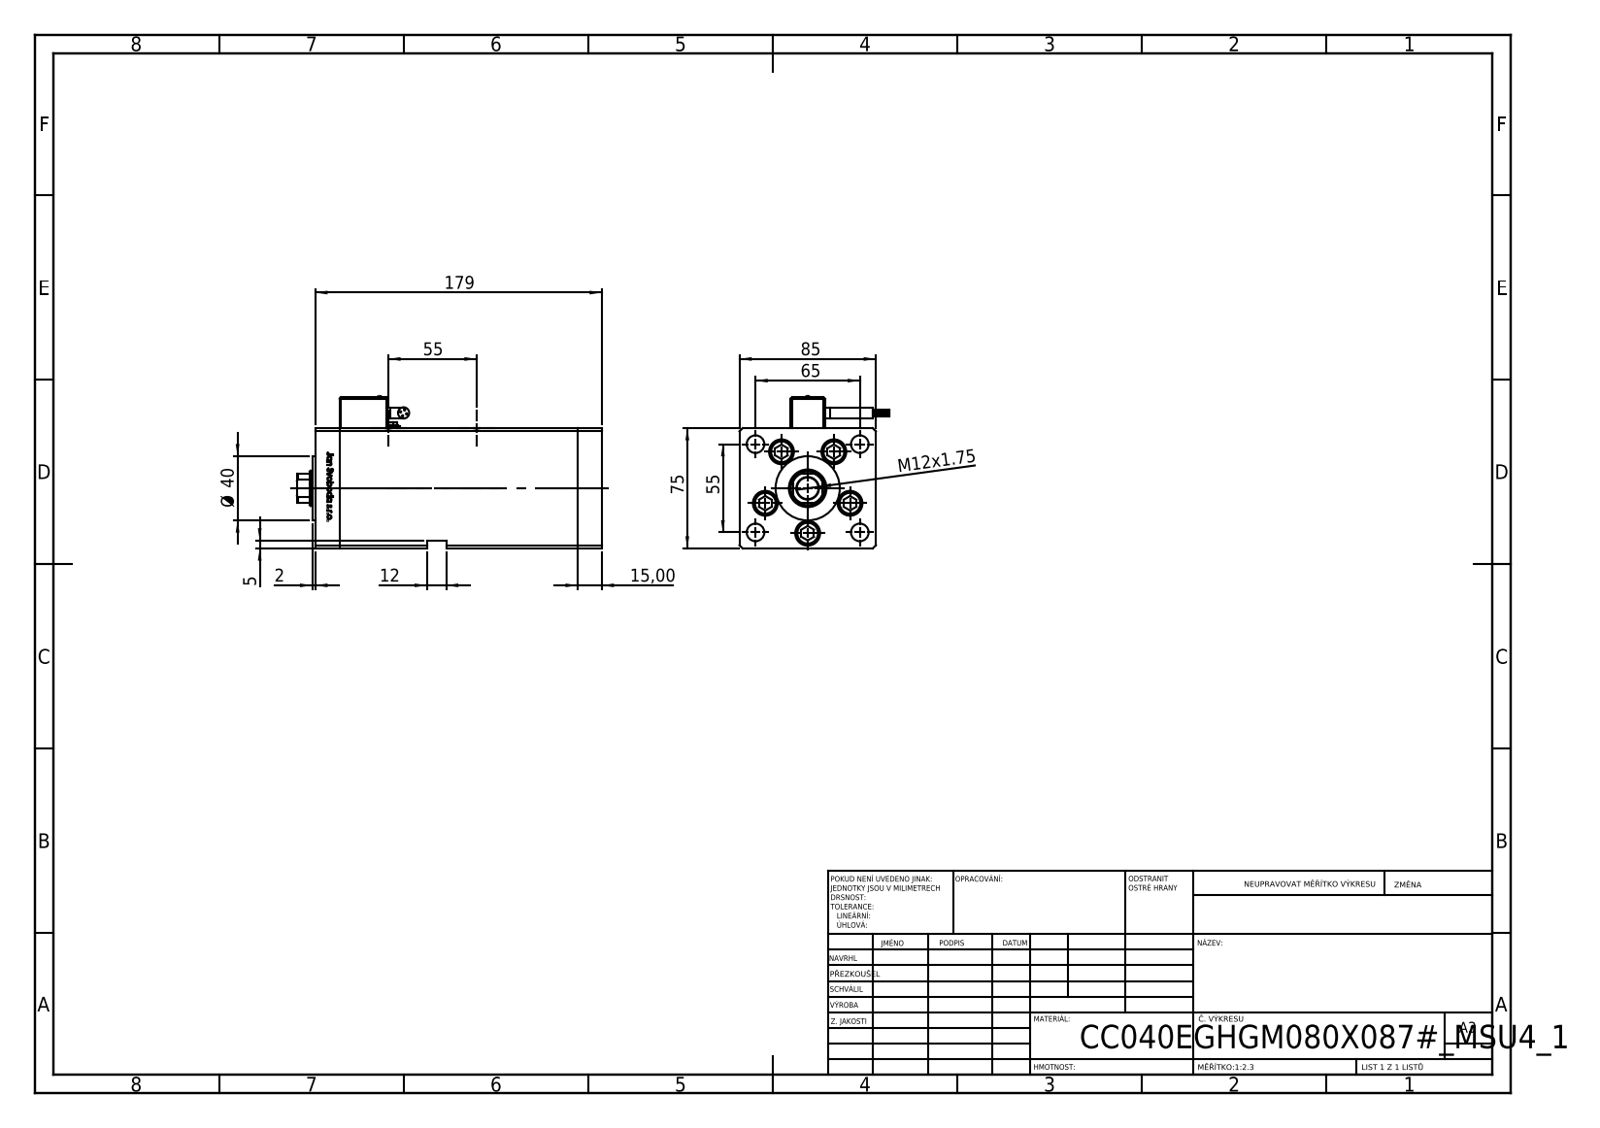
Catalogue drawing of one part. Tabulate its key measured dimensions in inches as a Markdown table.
| quantity | value |
| --- | --- |
| part name | V220C_FRONT_E; V220C_E MIDDLE; V220C BACK_E; Magnetic_Switch_MSU4 (+2 more) |
| STEP written by | SolidWorks 2019 (CONFIG_CONTROL_DESIGN) |
| units | inches |
| bodies | 15 solids, 1314 faces (512 planar, 210 cylindrical, 592 other) |
| overall size | 7.48 × 3.744 × 3.673 |
| volume | 60.35 in³ |
| surface area | 275.6 in² |
| round holes (diameter × count) | 0.433 × 9, 0.61 × 5, 0.413 × 4, 0.65 × 4, 0.079 × 2, 0.518 × 2, 0.142 × 1, 0.197 × 1, 0.276 × 1, 0.531 × 1, 0.866 × 1, 0.925 × 1 |
| round bosses / shafts (diameter × count) | 0.571 × 5, 0.315 × 5, 0.033 × 4, 0.276 × 2, 1.575 × 1, 0.236 × 1, 0.138 × 1, 0.098 × 1 |
| partial cylindrical surfaces (radius × count) | 0.039 × 14, 0.037 × 2, 0.157 × 2, 0.413 × 1 |
| main face-to-face distances | 3.346, 2.953, 0.591, 5.846, 6.437, 7.028, 1.348, 2.697, 0.413, 0.758 |
| hole center spacings | 1.102, 1.676, 2.165, 2.559, 3.352, 0.664, 0.755, 1.273 |
